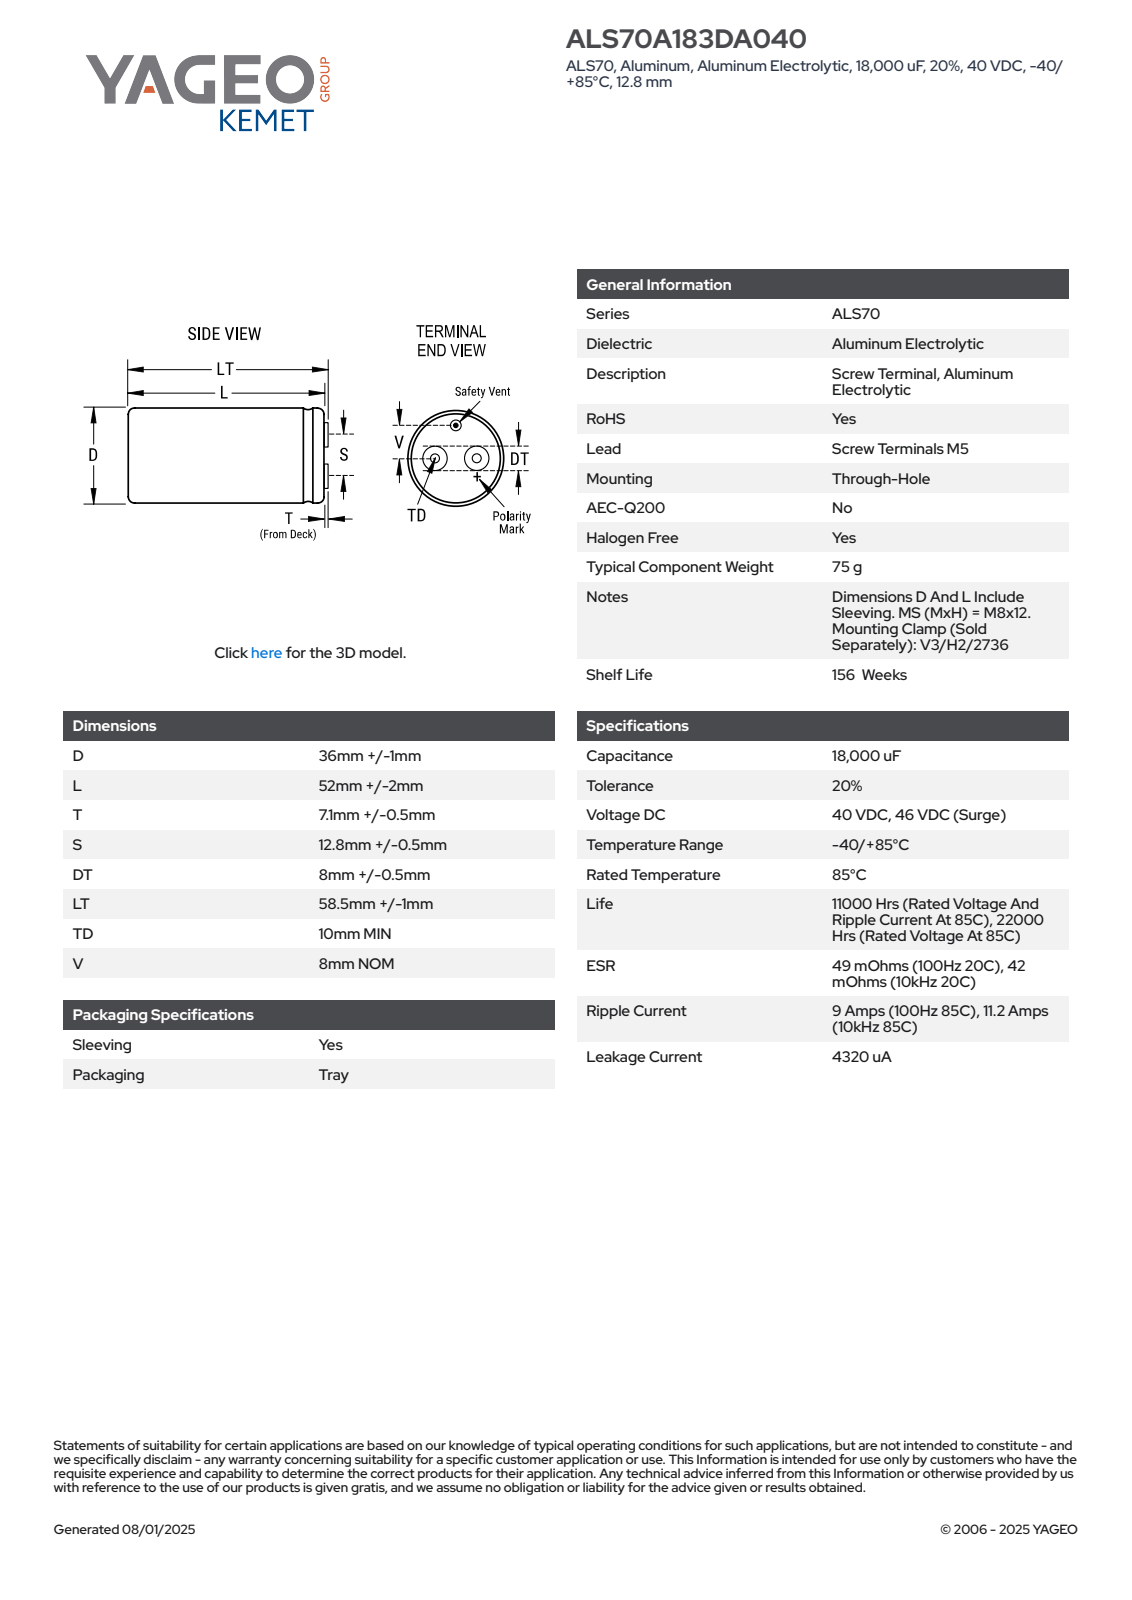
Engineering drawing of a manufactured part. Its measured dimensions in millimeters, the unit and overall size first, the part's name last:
Units: millimetres
Overall size (bounding box): 61.6 × 37.01 × 37
Round holes (diameter × count): ⌀5 ×2, ⌀1.33 ×1
Round bosses / shafts (diameter × count): ⌀8.5 ×2, ⌀37 ×1, ⌀2.27 ×1
Partial cylindrical surfaces — rounded edges, fillets, slot ends (radius × count): R18.51 ×1
Main face-to-face distances: 54, 61.6, 7.6, 51.6, 2.4, 10, 54.35, 2.75, 0.35, 7.25
Hole centre spacings: 10.24, 12.8
Volume: 58 242 mm³ · Surface area: 8 958 mm²
Bodies: 1 solid, 88 faces (30 planar, 19 cylindrical, 39 other)
Part name (STEP PRODUCT): CARC_KAR_36X52_D37L54T7.6S12.8DT8.500TD10.000V8.000
STEP written by: SolidWorks 2014 (AUTOMOTIVE_DESIGN)
